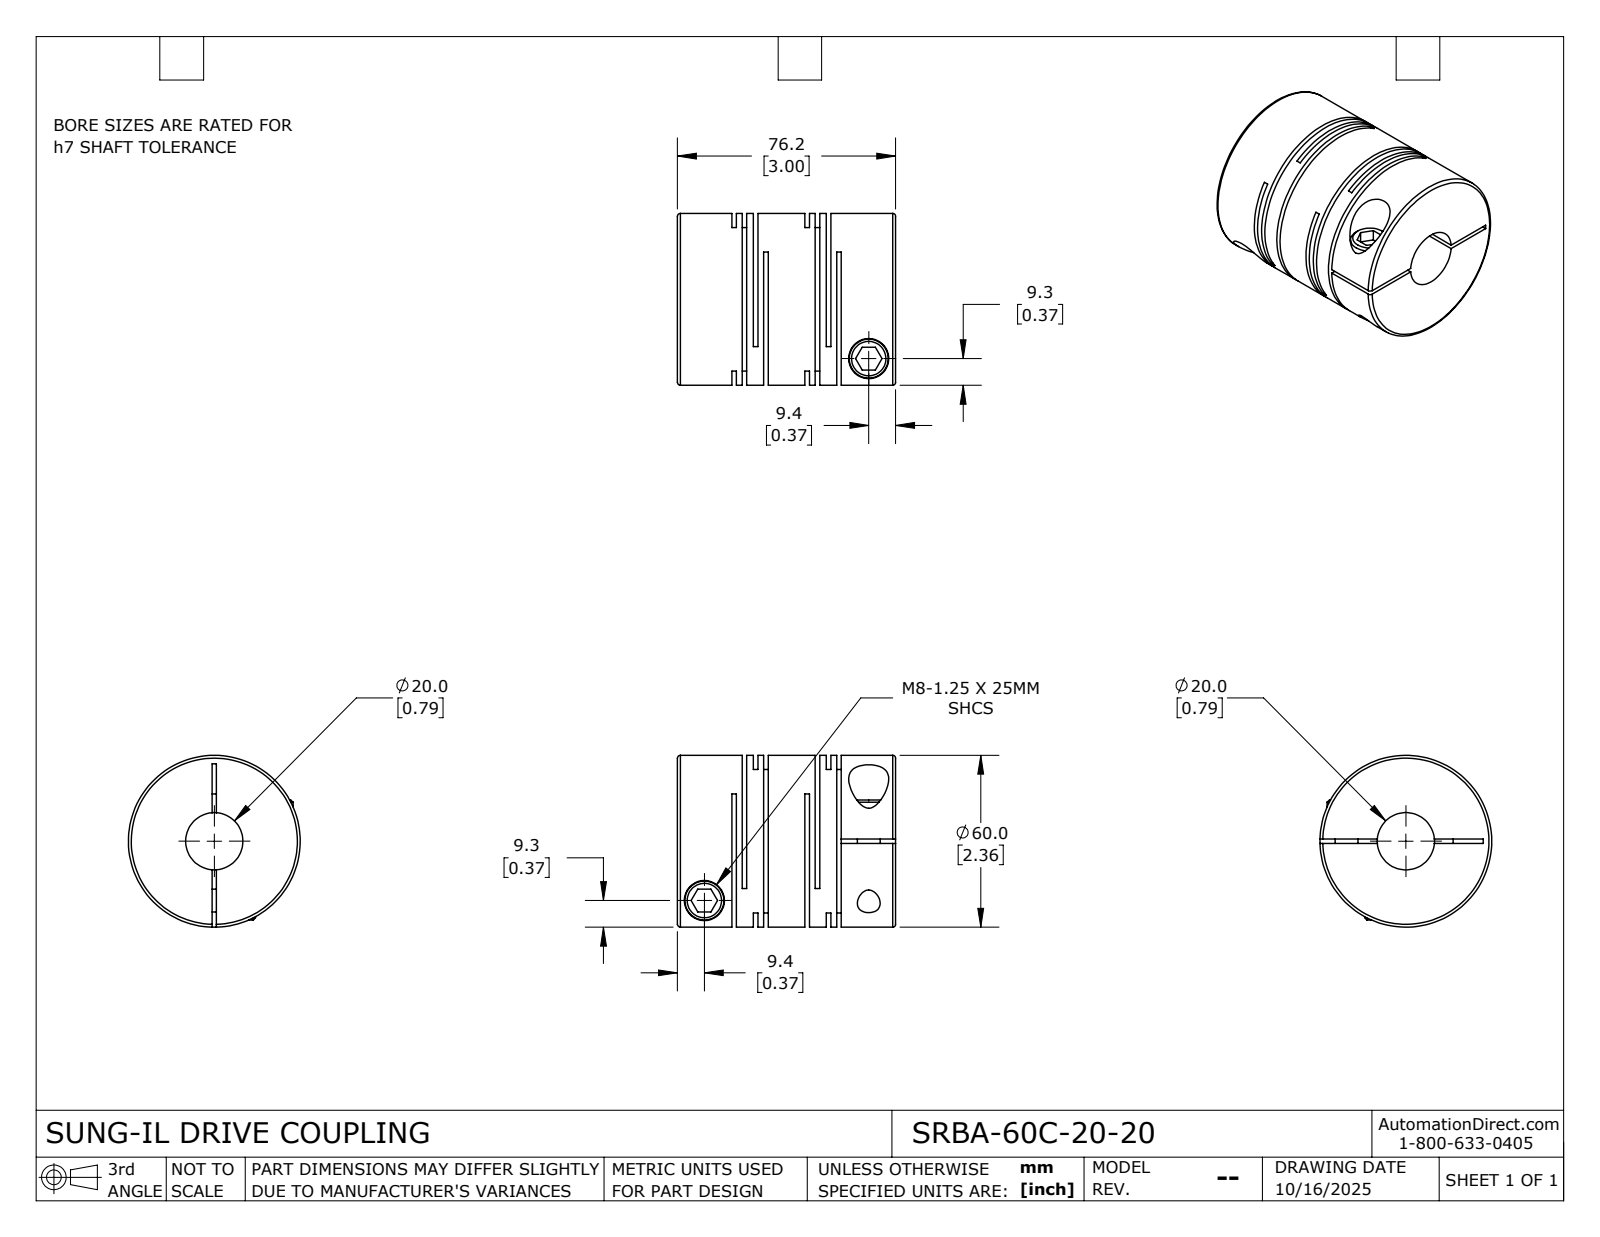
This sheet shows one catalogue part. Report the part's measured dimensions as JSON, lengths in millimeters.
{"part_name": "SRBA-60C-20-20", "step_written_by": "SolidWorks 2024 (CONFIG_CONTROL_DESIGN)", "units": "millimeters", "bodies": {"solids": 1, "faces": 115, "planar": 60, "cylindrical": 42, "other": 13}, "overall_size": [76.2, 60, 60], "volume_mm3": 160278, "surface_area_mm2": 59121, "round_holes": [[8, 2], [14, 2], [20, 1]], "round_bosses_or_shafts": [[13.6, 2], [60, 1]], "face_to_face_distances": [1.6, 3.6, 7.5, 25.5, 33, 2, 5.9, 23.9, 3.9, 18]}
